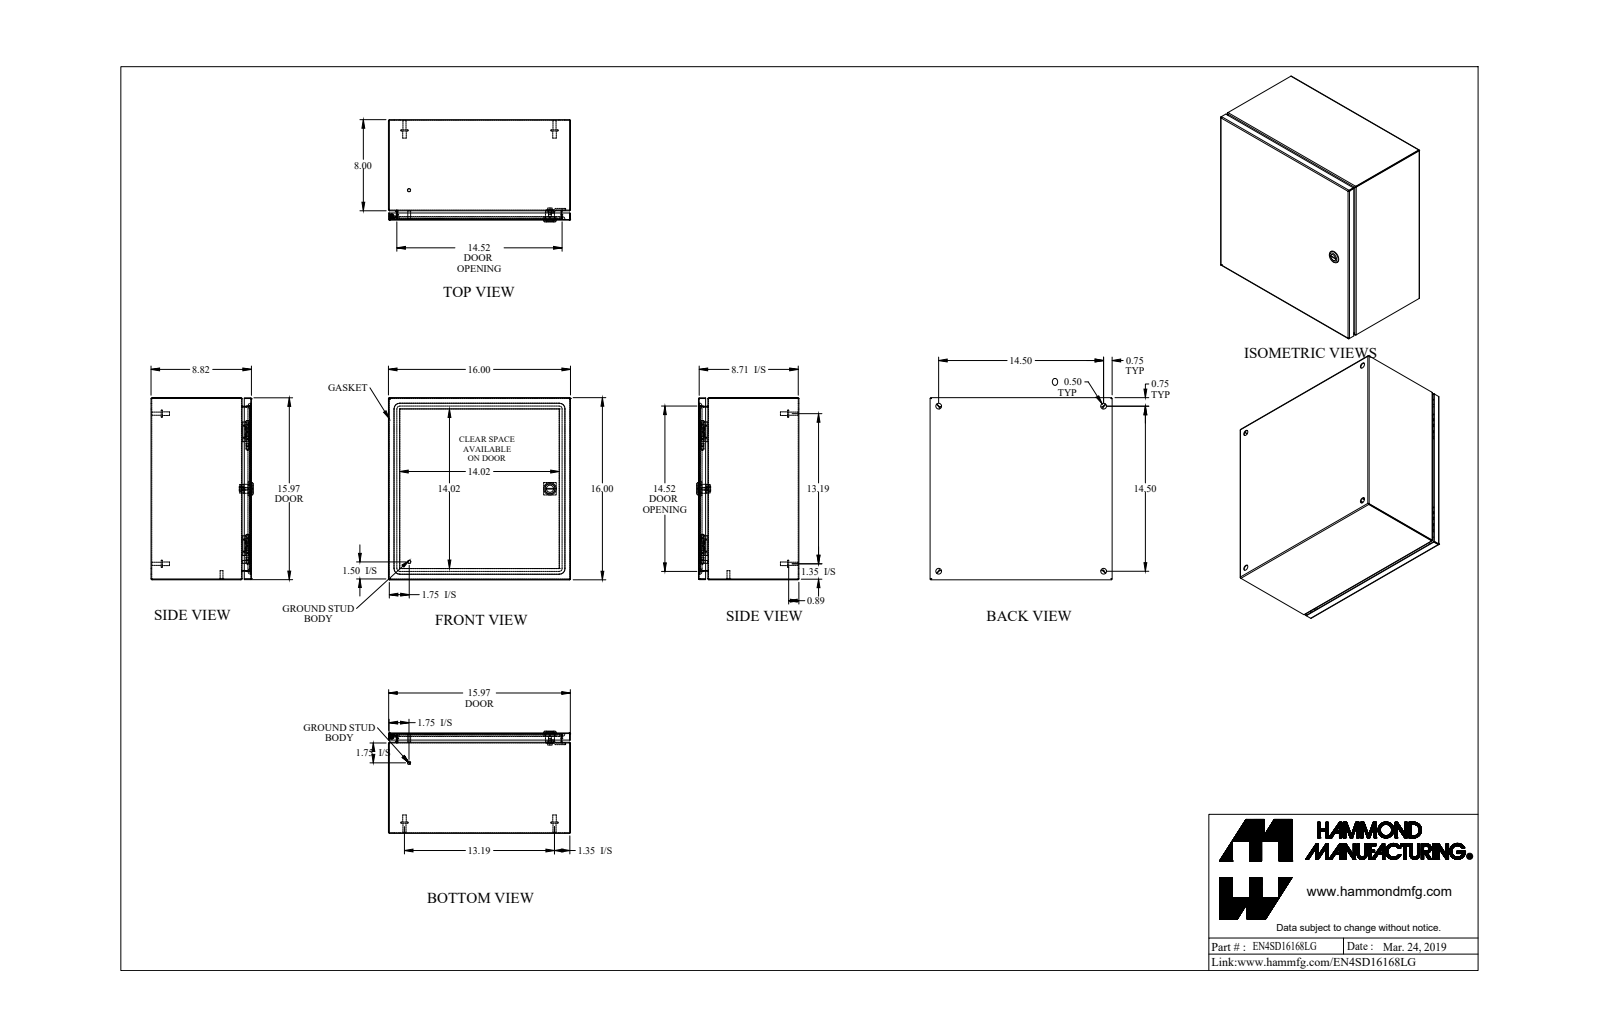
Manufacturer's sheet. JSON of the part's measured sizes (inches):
{"part_name": "EN4SD16168LG_Default", "step_written_by": "SolidWorks 2019 (CONFIG_CONTROL_DESIGN)", "units": "inches", "bodies": {"solids": 21, "faces": 634, "planar": 285, "cylindrical": 213, "other": 136}, "overall_size": [16, 16, 8.982], "volume_in3": 71.9, "surface_area_in2": 2440, "round_holes": [[0.5, 4], [0.172, 1], [0.232, 1], [0.24, 1], [0.242, 1], [0.625, 1], [0.785, 1]], "round_bosses_or_shafts": [[0.625, 4], [0.313, 4], [0.27, 4], [0.281, 2], [0.25, 2], [1.1, 1], [0.525, 1], [0.455, 1]], "partial_cylinders_radius": [[0.029, 21], [0.086, 21], [0.25, 16], [19, 8], [0.006, 4], [0.062, 4], [0.499, 4], [0.125, 2]], "face_to_face_distances": [0.057, 8.765, 15.943, 15.886, 8.708, 8.822, 16, 0.822, 7.943, 0.749], "hole_center_spacings": [14.5, 20.506, 7.326, 7.327, 15.271, 15.272]}
